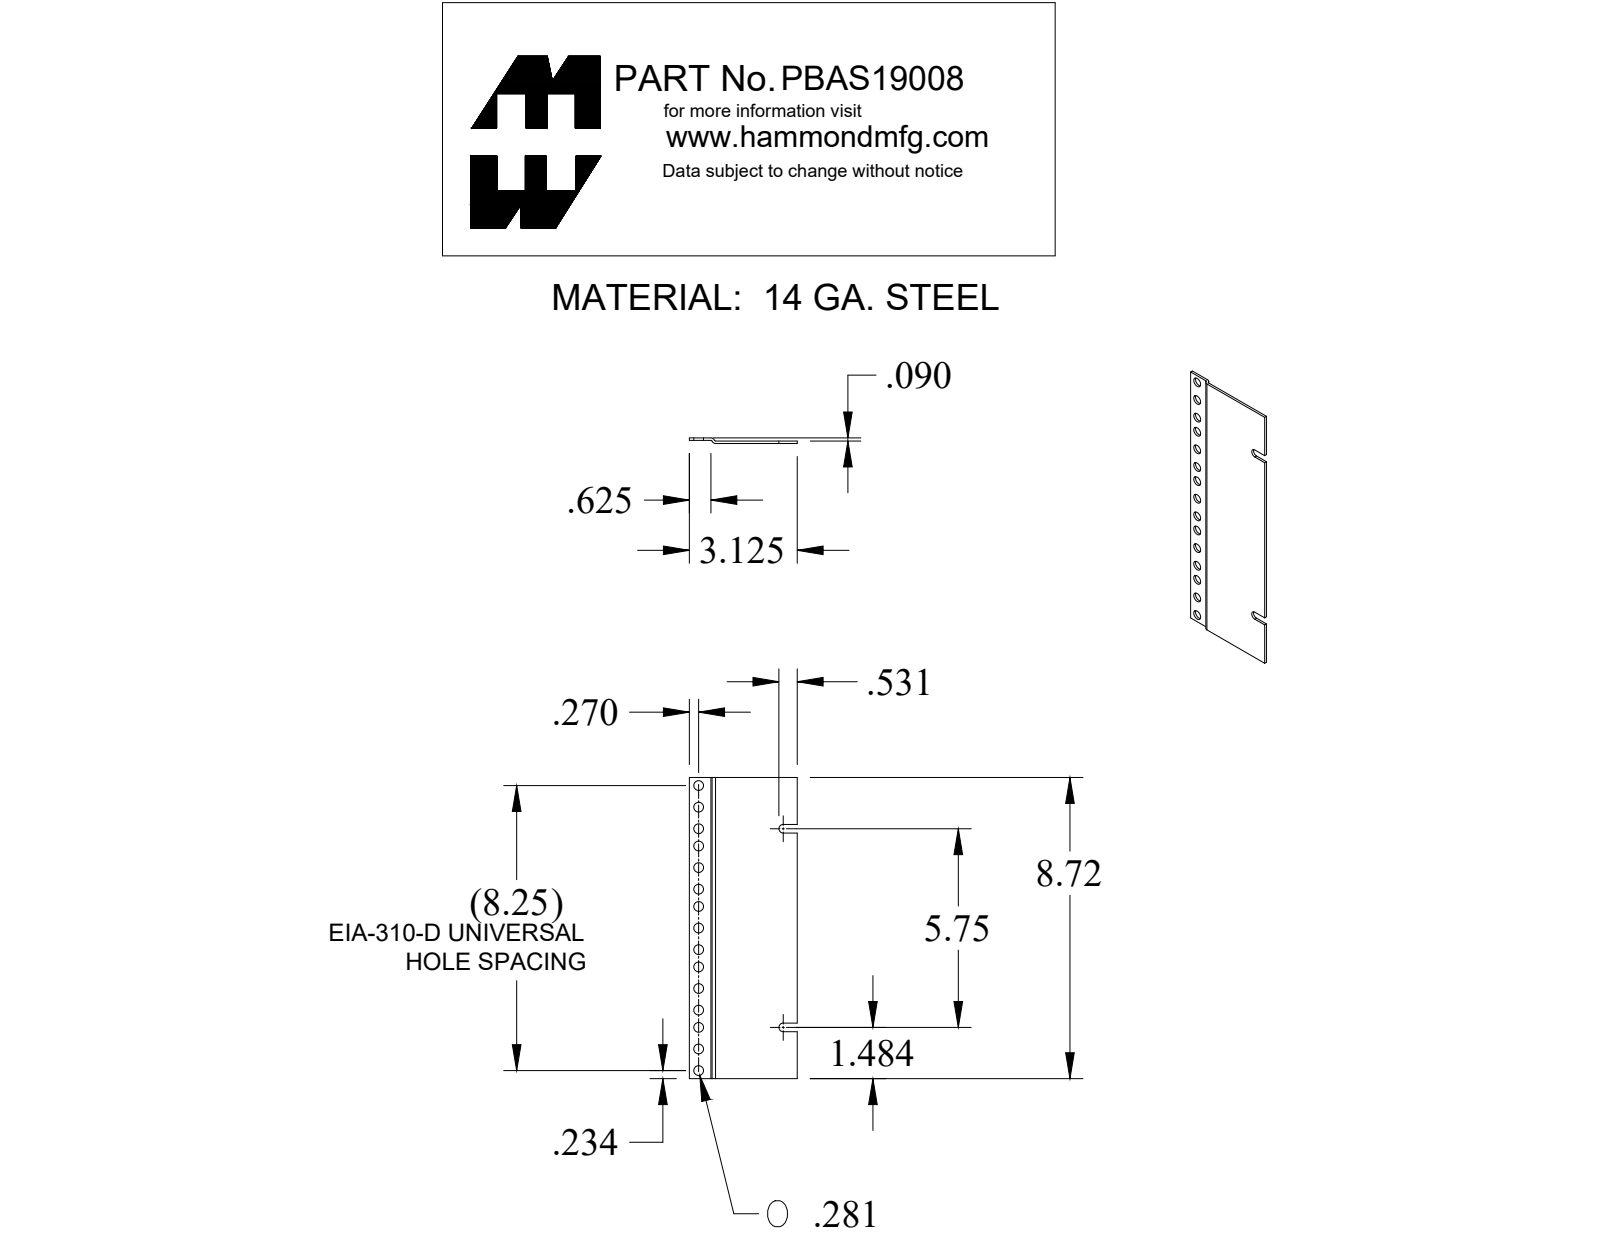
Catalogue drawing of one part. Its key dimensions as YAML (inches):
part_name: "PBAS19008BK2"
step_written_by: "SolidWorks 2019 (CONFIG_CONTROL_DESIGN)"
units: inches
bodies: {solids: 1, faces: 35, planar: 14, cylindrical: 21, other: 0}
overall_size: [8.718, 3.125, 0.162]
volume: 1.9
surface_area: 55.58
round_holes:
  - {diameter: 0.281, count: 15}
partial_cylinders:
  - {radius: 0.036, count: 2}
  - {radius: 0.108, count: 2}
  - {radius: 0.125, count: 2}
face_to_face_distances: [0.072, 0.09, 0.162, 0.018, 0.09, 0.072, 3.125, 8.718, 1.359, 7.359]
hole_center_spacings: [1.75, 0.625, 1.125, 2.875, 3.5, 0.625, 1.25, 2.375]
